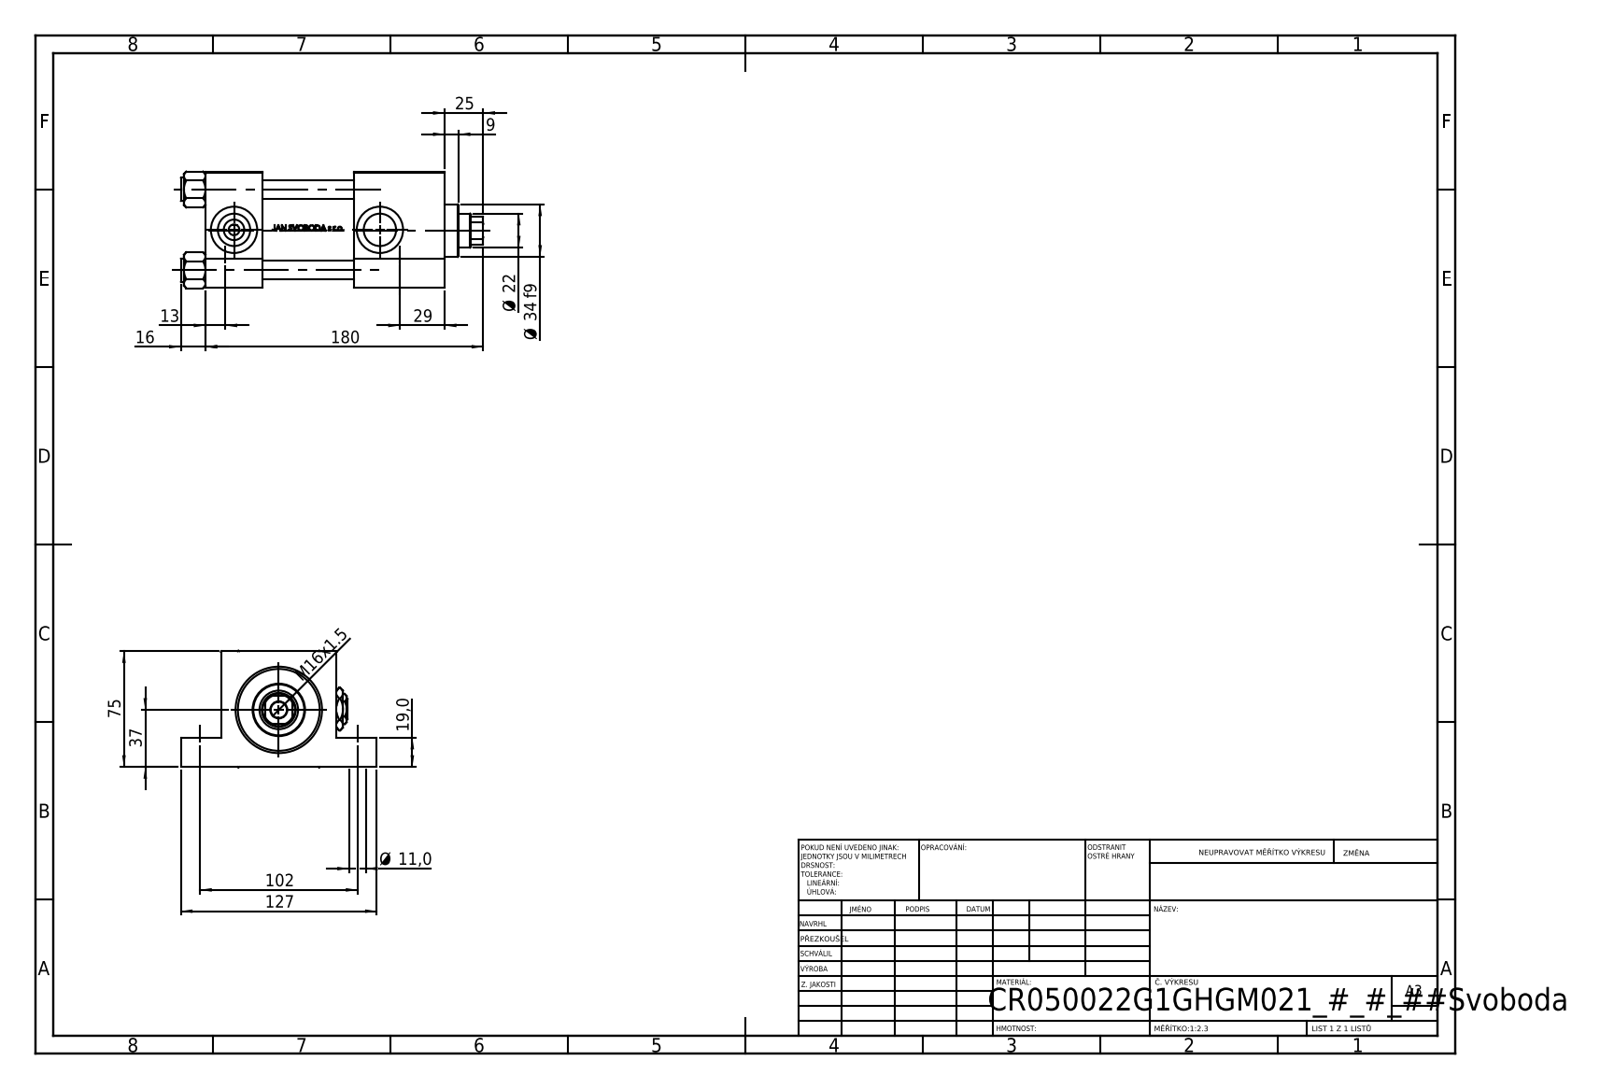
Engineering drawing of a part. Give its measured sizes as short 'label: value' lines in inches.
name: V215CR_G_Body; V215CR_VCP_G; NUT_M5_G; V215_VC_A (+2 more)
written by: SolidWorks 2019 (CONFIG_CONTROL_DESIGN)
unit: in
bodies: 12 solids, 1134 faces (454 planar, 128 cylindrical, 552 other)
size: 7.717 × 5 × 2.974
volume: 46 in³; area: 250.9 in²
holes: 4× ⌀0.433, 4× ⌀0.472, 2× ⌀0.276, 2× ⌀0.825, 2× ⌀1.181, 1× ⌀0.413, 1× ⌀0.866, 1× ⌀0.984, 1× ⌀1.614, 1× ⌀1.969, 1× ⌀2.087
bosses: 4× ⌀0.591, 1× ⌀2.205, 1× ⌀1.339
rounds: 1× R0.413
face distances: 2.953, 2.323, 1.457, 6.102, 4.646, 0.748, 2.205, 3.78, 1.024, 3.976
hole spacings: 2.059, 1.442, 1.47, 2.912, 4.016, 4.449, 5.993, 3.72
